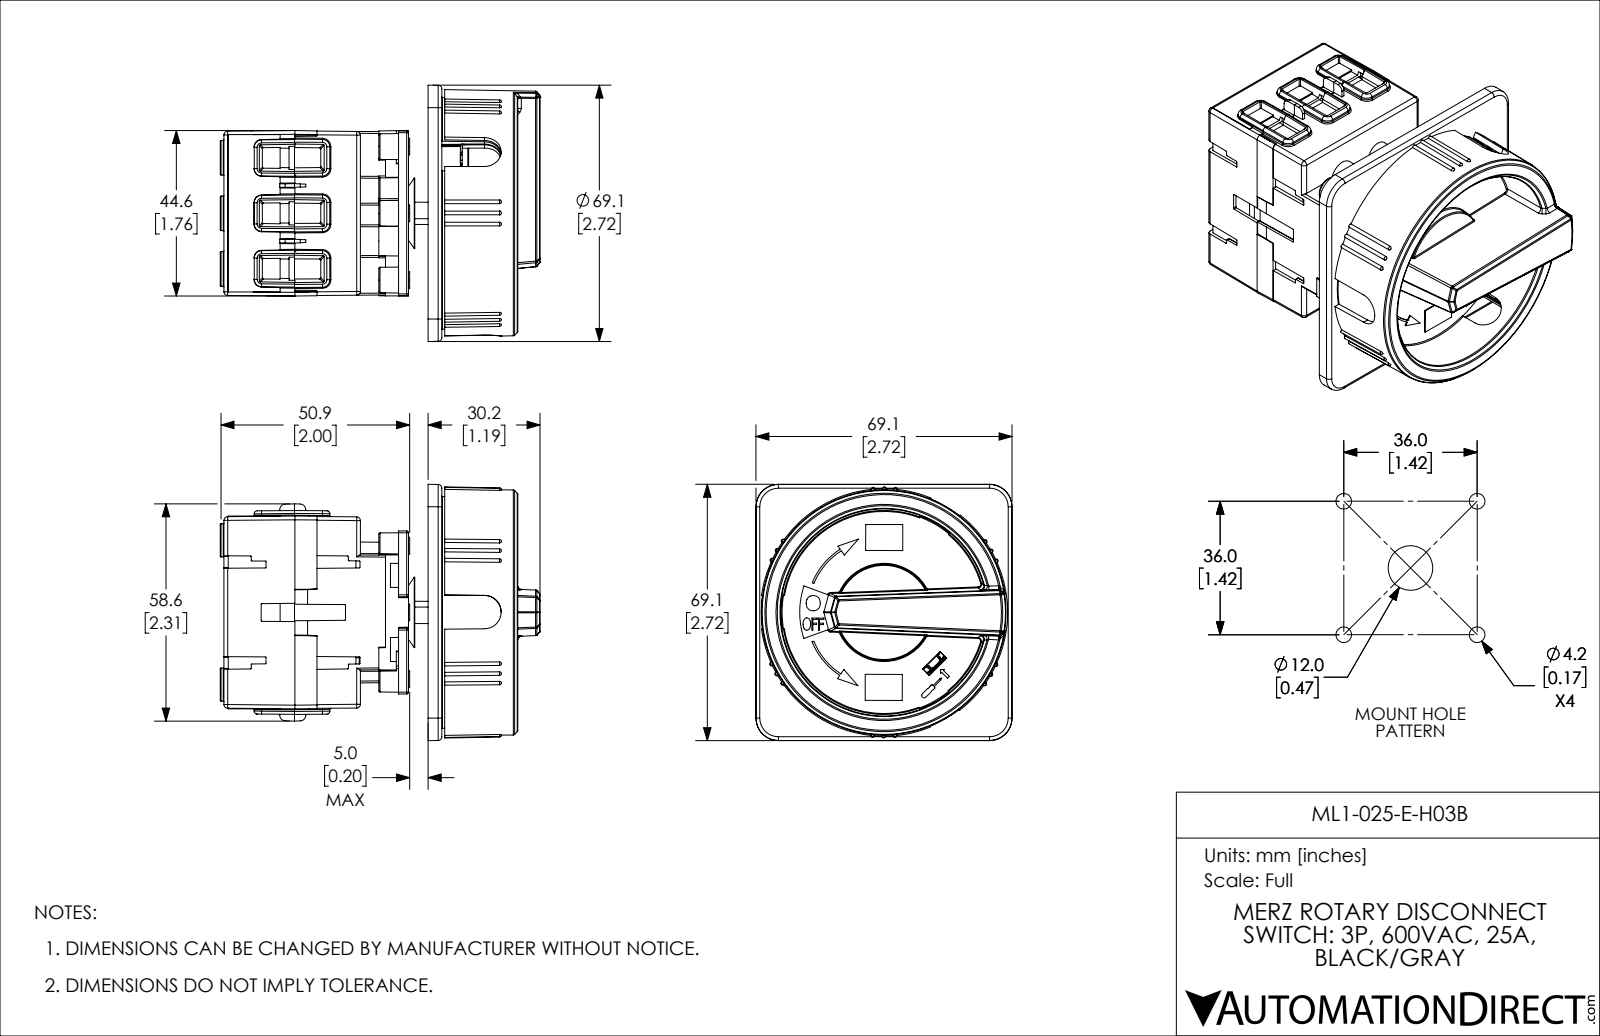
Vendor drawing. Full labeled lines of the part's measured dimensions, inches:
Part name (STEP PRODUCT): ML1-025-E-H03B
STEP written by: SolidWorks 2019 (AUTOMOTIVE_DESIGN)
Units: inches
Bodies: 1 solid, 2964 faces (1185 planar, 610 cylindrical, 1169 other)
Overall size (bounding box): 3.398 × 2.722 × 2.722
Volume: 8.361 in³ · Surface area: 101.4 in²
Round bosses / shafts (diameter × count): ⌀0.071 ×2, ⌀0.748 ×1, ⌀0.236 ×1
Partial cylindrical surfaces — rounded edges, fillets, slot ends (radius × count): R0.02 ×132, R0.012 ×68, R0.039 ×50, R0.008 ×44, R0.008 ×41, R0.01 ×39, R0.031 ×34, R0.079 ×12
Main face-to-face distances: 0.059, 0.138, 0.197, 0.079, 0.276, 0.571, 0.02, 0.551, 0.295, 0.807
